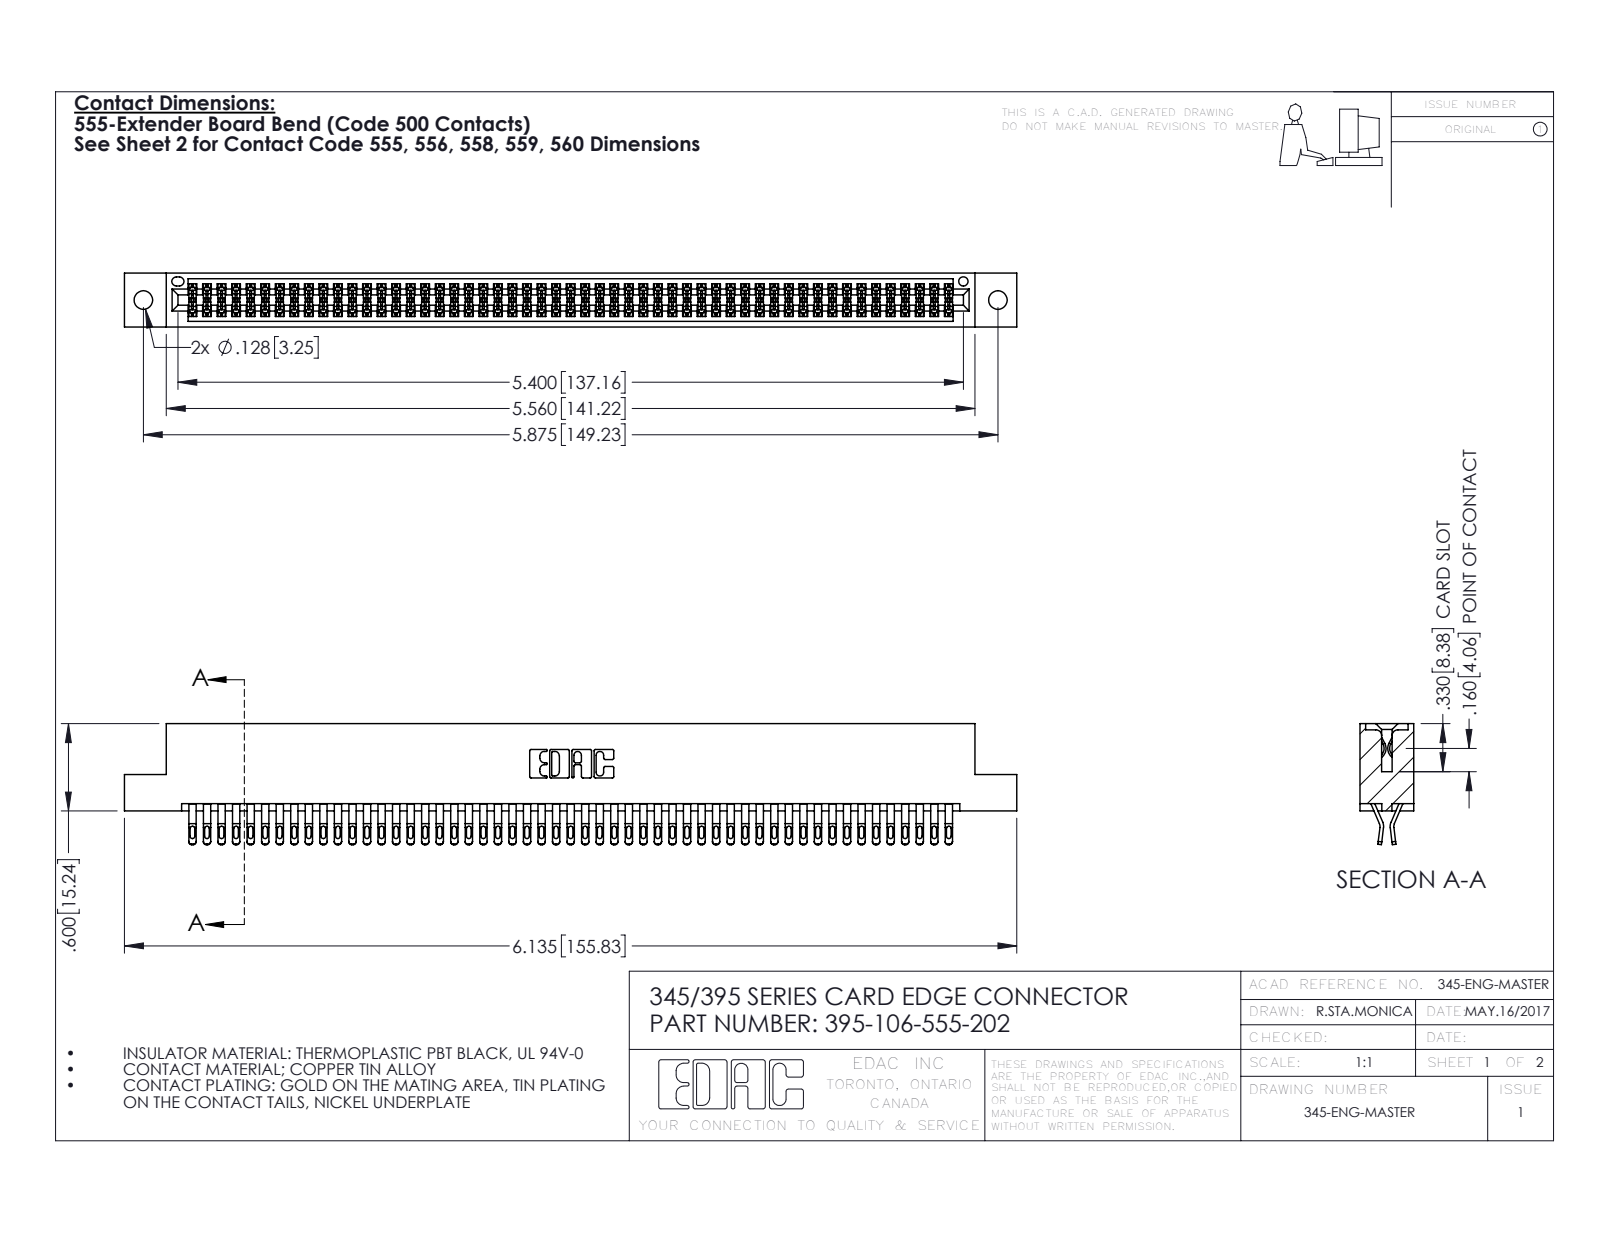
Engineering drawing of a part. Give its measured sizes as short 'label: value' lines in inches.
name: 345-292-001_555 Tail; 395-106-555-202; 345 Part_Flush Mounting Lugs - 0.128 Dia
written by: SolidWorks 2016 (CONFIG_CONTROL_DESIGN)
unit: in
bodies: 107 solids, 6062 faces (3366 planar, 2696 cylindrical, 0 other)
size: 6.135 × 0.832 × 0.37
volume: 0.946 in³; area: 37.1 in²
holes: 2× ⌀0.128, 1× ⌀0.064
rounds: 265× R0.016, 212× R0.02, 159× R0.006, 22× R0.01, 6× R0.007, 6× R0.031, 3× R0.026, 2× R0.01
face distances: 0.298, 0.072, 0.025, 0.37, 0.2, 0.098, 0.272, 0.225, 0.175, 0.149
hole spacings: 0.27, 5.639, 5.875
